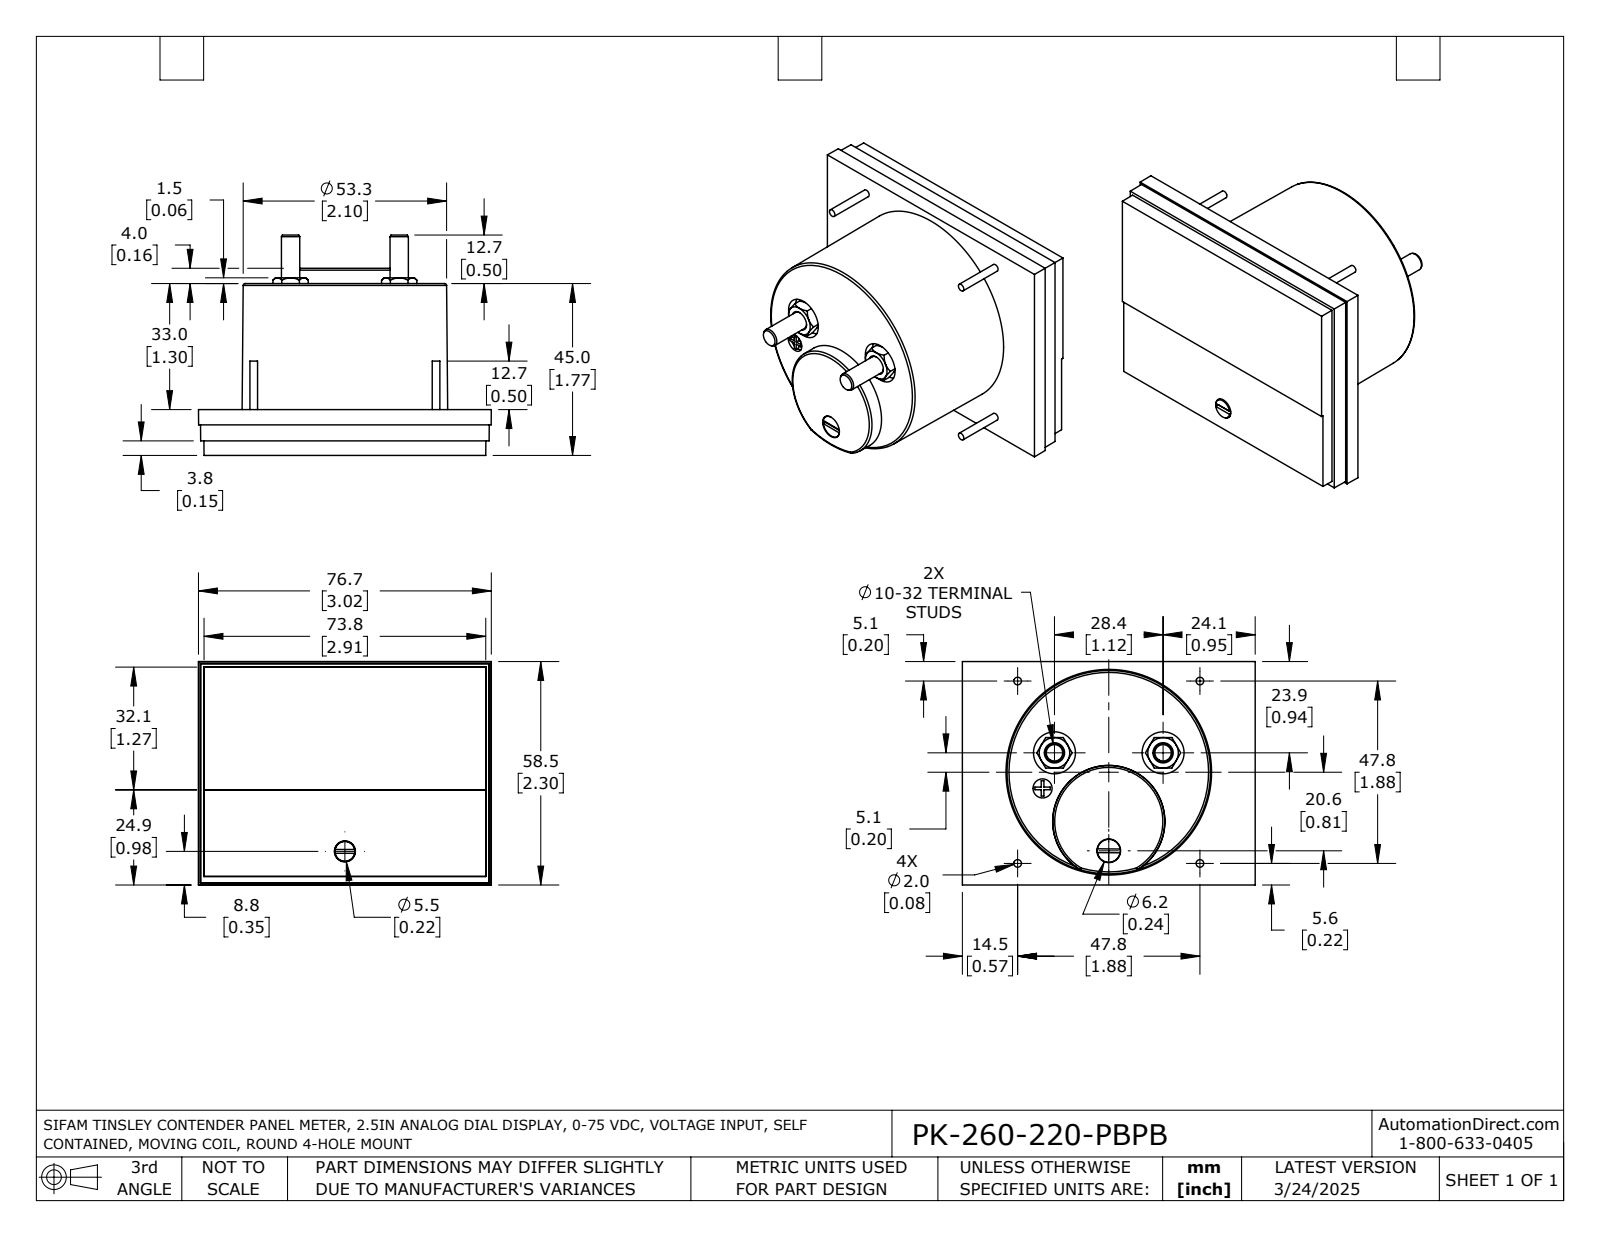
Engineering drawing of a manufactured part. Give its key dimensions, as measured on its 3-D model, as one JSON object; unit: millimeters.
{"part_name": "PK-260-220-PBPB", "step_written_by": "SolidWorks 2021 (AUTOMOTIVE_DESIGN)", "units": "millimeters", "bodies": {"solids": 1, "faces": 192, "planar": 95, "cylindrical": 37, "other": 60}, "overall_size": [76.7, 58.5, 57.7], "volume_mm3": 125500, "surface_area_mm2": 23580, "round_holes": [[5, 3], [11, 2], [5.3, 1], [5.5, 1], [6.2, 1]], "round_bosses_or_shafts": [[2, 4], [4.8, 2], [6, 1], [5.2, 1]], "partial_cylinders_radius": [[0.8, 1]], "face_to_face_distances": [0.5, 12, 3.3, 8.2, 3.8, 11.5, 1.4, 2, 10.1, 1.9], "hole_center_spacings": [29.3, 29.5, 9.8, 23.8, 23.9, 28.4, 32.9]}
